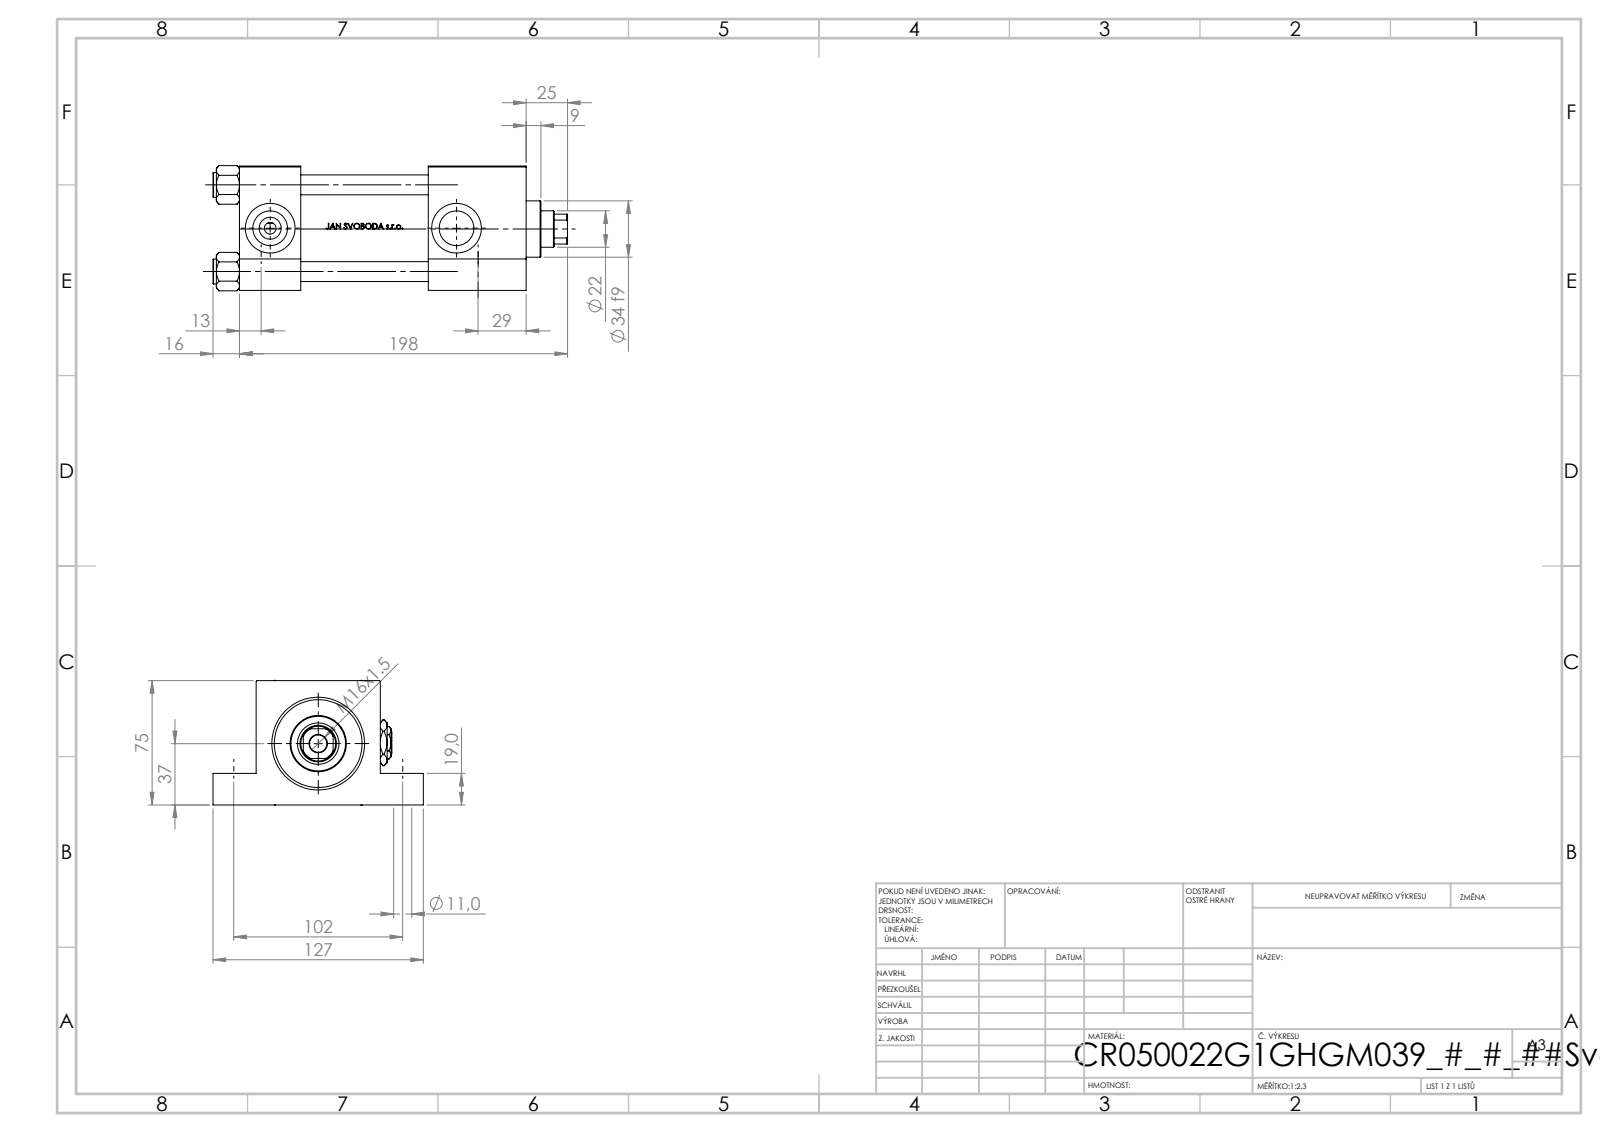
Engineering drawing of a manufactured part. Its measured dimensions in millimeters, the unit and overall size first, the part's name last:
Units: millimetres
Overall size (bounding box): 214 × 127 × 75.54
Round holes (diameter × count): ⌀11 ×4, ⌀12 ×4, ⌀7 ×2, ⌀20.96 ×2, ⌀30 ×2, ⌀10.5 ×1, ⌀22 ×1, ⌀25 ×1, ⌀41 ×1, ⌀50 ×1, ⌀53 ×1
Round bosses / shafts (diameter × count): ⌀15 ×4, ⌀56 ×1, ⌀34 ×1
Partial cylindrical surfaces — rounded edges, fillets, slot ends (radius × count): R10.5 ×1
Main face-to-face distances: 75, 37, 173, 136, 19, 56, 114, 77, 59, 26
Hole centre spacings: 52.3, 36.63, 37.34, 73.96, 102, 131, 166.03, 112.5
Volume: 777 712 mm³ · Surface area: 171 809 mm²
Bodies: 12 solids, 1134 faces (454 planar, 128 cylindrical, 552 other)
Part name (STEP PRODUCT): V215CR_VCP_G; V215CR_G_TYCINKA; V215_VC_A; NUT_M5_G (+2 more)
STEP written by: SolidWorks 2019 (CONFIG_CONTROL_DESIGN)
